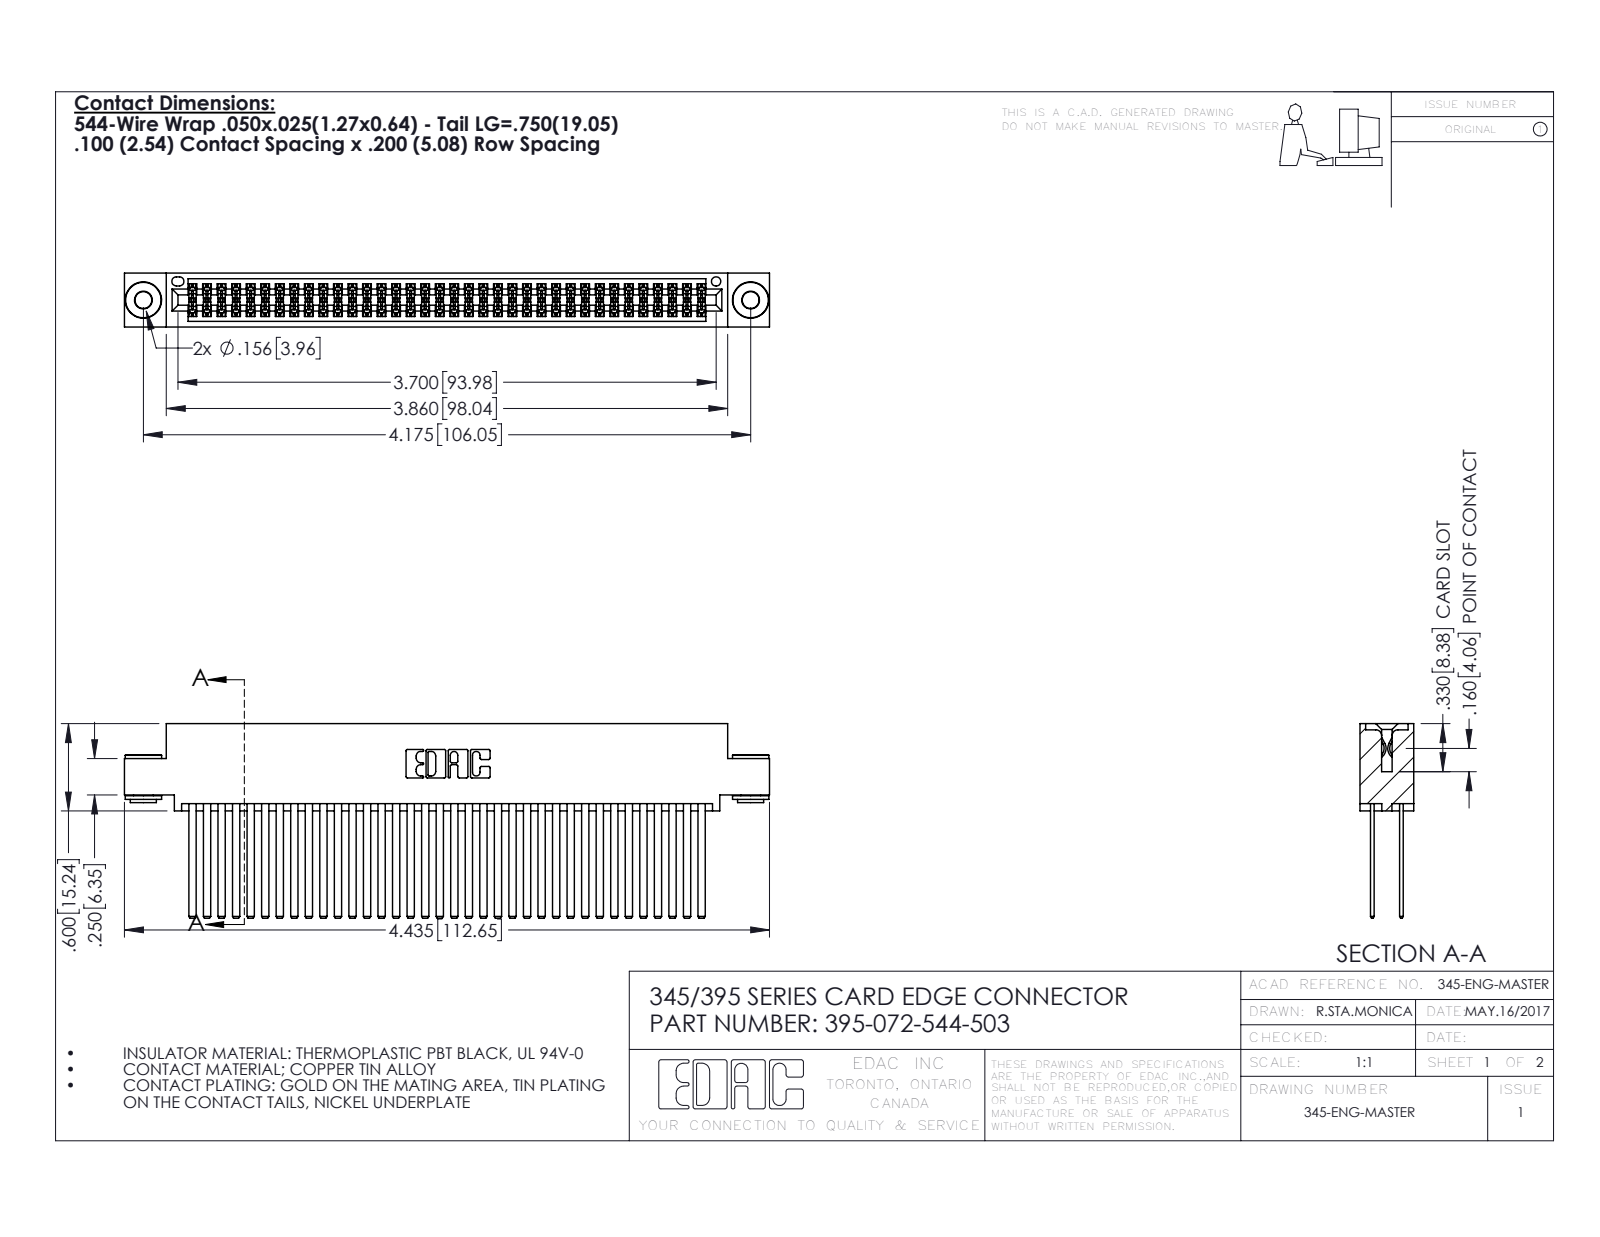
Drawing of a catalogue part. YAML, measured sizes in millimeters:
part_name: "345-250-002_345-250-002-102; 345 Part_0.110 Offset - 0.156 Dia-TH; 345-292-001_345-293-144; 395-072-544-503"
step_written_by: "SolidWorks 2016 (CONFIG_CONTROL_DESIGN)"
units: millimeters
bodies: {solids: 75, faces: 3336, planar: 2182, cylindrical: 1146, other: 8}
overall_size: [112.6, 34, 9.4]
volume: 11800
surface_area: 20650
round_holes:
  - {diameter: 2.9, count: 2}
  - {diameter: 4, count: 2}
  - {diameter: 1.6, count: 1}
round_bosses_or_shafts:
  - {diameter: 6.4, count: 2}
  - {diameter: 4.6, count: 2}
  - {diameter: 3.5, count: 2}
partial_cylinders:
  - {radius: 0.2, count: 108}
  - {radius: 0.3, count: 22}
  - {radius: 0.2, count: 6}
  - {radius: 0.8, count: 6}
  - {radius: 0.7, count: 3}
  - {radius: 0.4, count: 2}
  - {radius: 0.5, count: 2}
  - {radius: 0.6, count: 2}
face_to_face_distances: [5.1, 0.6, 1.8, 2.5, 6.9, 7.6, 5.7, 4.4, 9.4, 1.3]
hole_center_spacings: [6.9, 100.1, 106]
